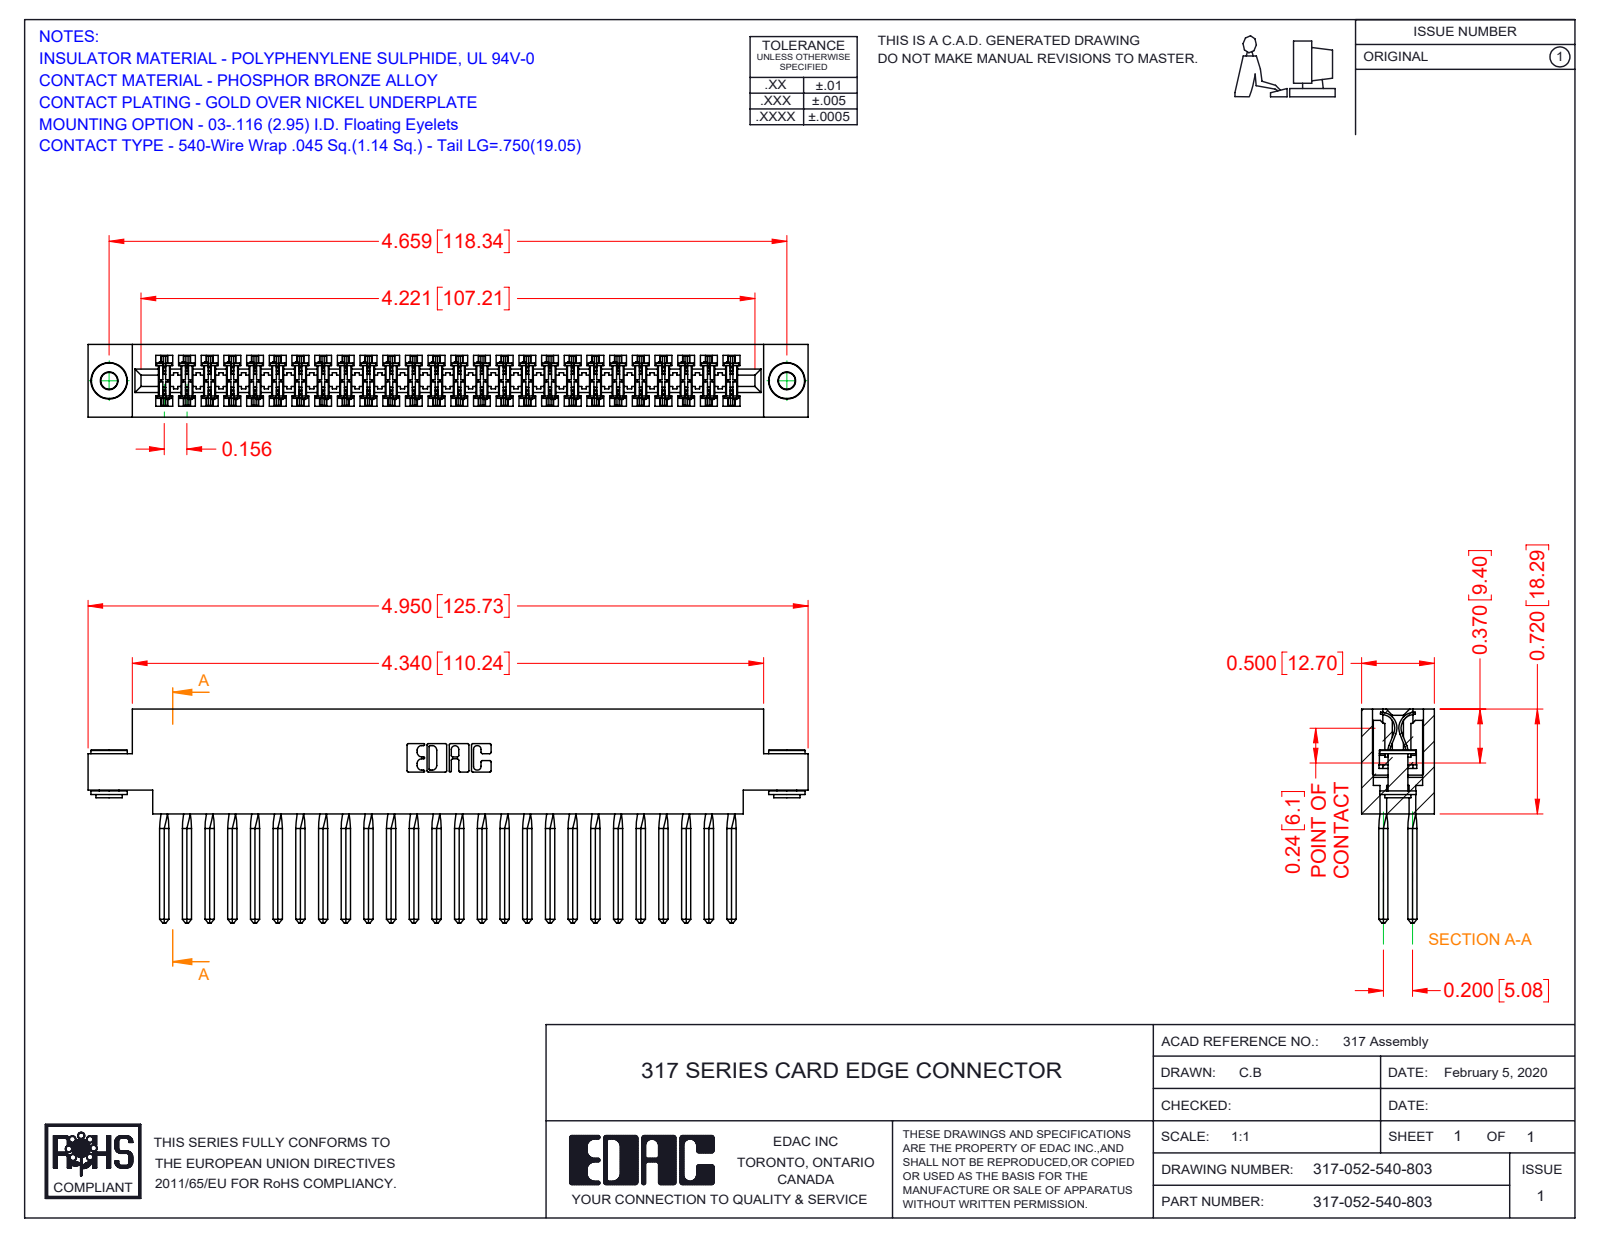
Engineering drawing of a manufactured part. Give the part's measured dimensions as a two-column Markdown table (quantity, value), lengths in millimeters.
| quantity | value |
| --- | --- |
| part name | 317-290-001_540; 317 Part_.156 Dia - TH; 345-250-002_345-250-002-102; 317-052-540-803 |
| STEP written by | SolidWorks 2016 (CONFIG_CONTROL_DESIGN) |
| units | millimeters |
| bodies | 55 solids, 4768 faces (3864 planar, 688 cylindrical, 216 other) |
| overall size | 125.7 × 37.3 × 12.7 |
| volume | 20 580 mm³ |
| surface area | 30 290 mm² |
| round holes (diameter × count) | 2.9 × 2, 4 × 2 |
| round bosses / shafts (diameter × count) | 6.4 × 2, 4.6 × 2, 3.5 × 2 |
| partial cylindrical surfaces (radius × count) | 0.4 × 104, 0.3 × 22, 0.2 × 6, 0.8 × 6, 0.7 × 3, 2.4 × 2, 2.5 × 2, 2.8 × 2 |
| main face-to-face distances | 12.7, 1.9, 10.8, 8.9, 2.8, 5, 2.4, 18.3, 5.1, 2.9 |
| hole center spacings | 118.3 |
